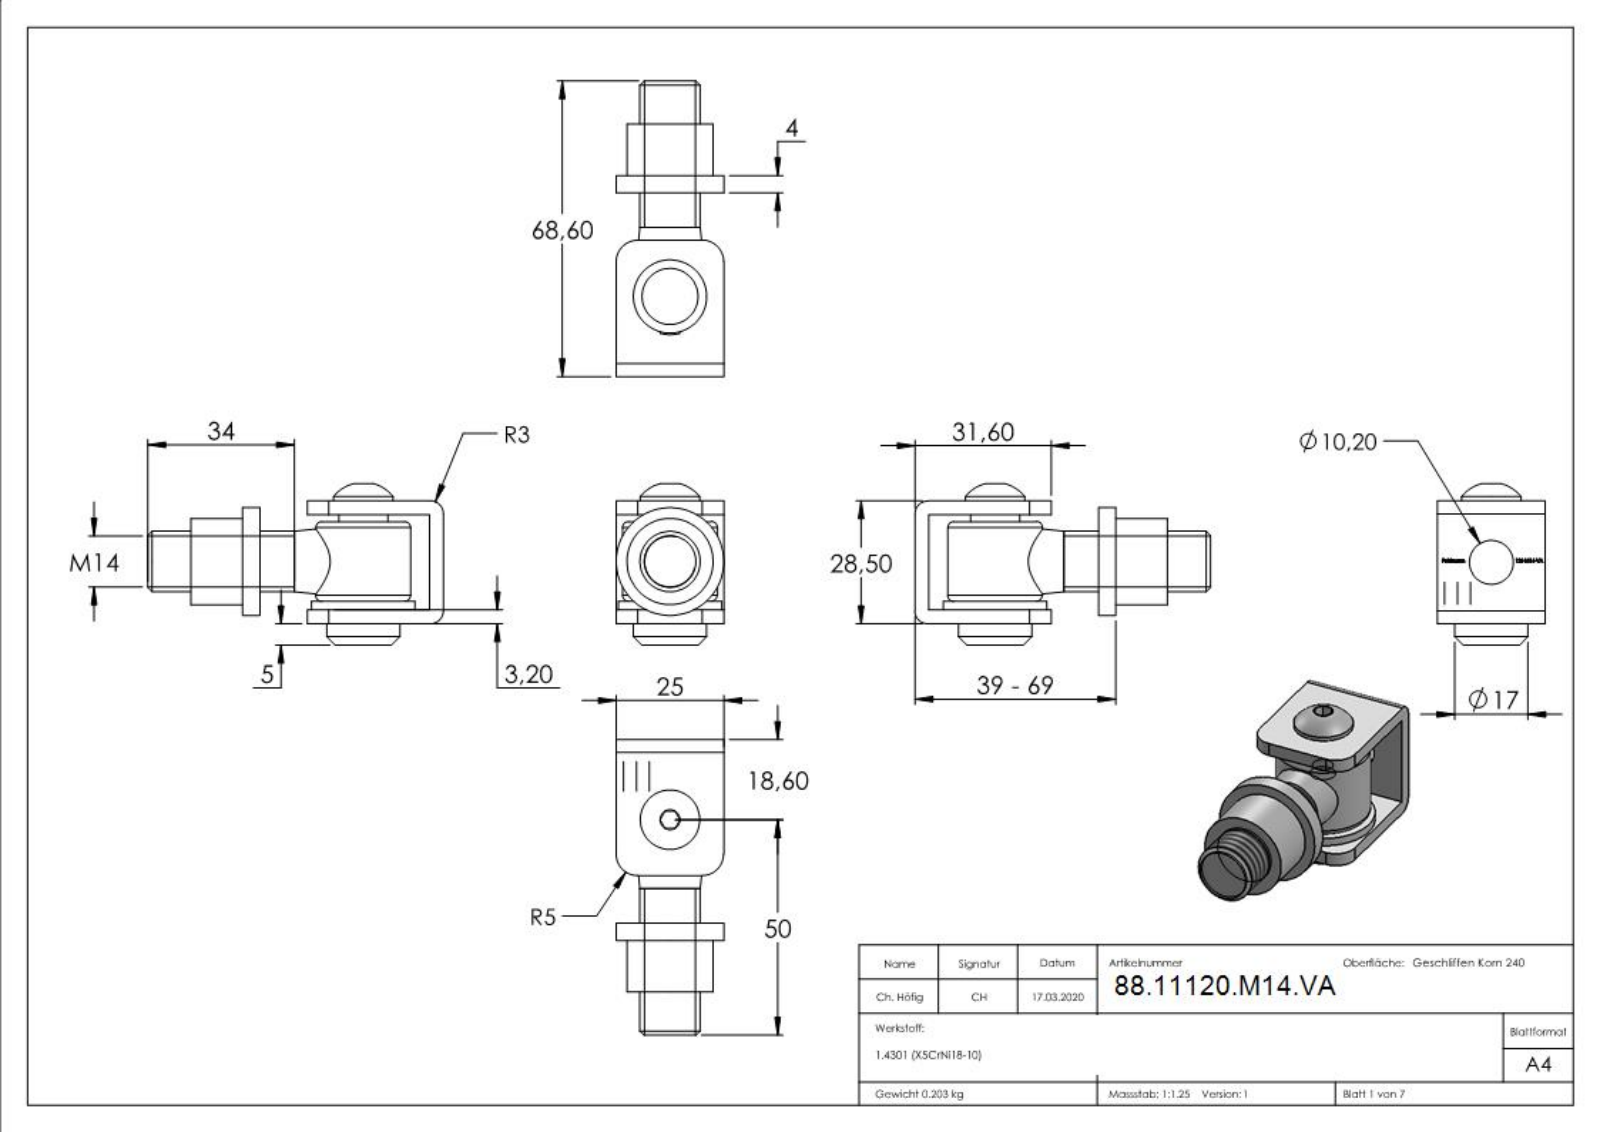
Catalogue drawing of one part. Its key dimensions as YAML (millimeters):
part_name: "120-M14-VA Teil5_120-M14-VA Teil5; 120-M14-VA Teil5; 120-M14-VA Teil1_120-M14-VA Teil1; 120-M14-VA Teil1 (+8 more)"
step_written_by: "SolidWorks 2015 (CONFIG_CONTROL_DESIGN)"
units: millimeters
bodies: {solids: 6, faces: 286, planar: 183, cylindrical: 24, other: 79}
overall_size: [68.6, 37.5, 25]
volume: 25665
surface_area: 14442
round_holes:
  - {diameter: 5, count: 1}
  - {diameter: 6.8, count: 1}
  - {diameter: 10.2, count: 1}
  - {diameter: 11.6, count: 1}
  - {diameter: 11.8, count: 1}
  - {diameter: 12, count: 1}
  - {diameter: 13, count: 1}
round_bosses_or_shafts:
  - {diameter: 25, count: 1}
  - {diameter: 24, count: 1}
  - {diameter: 22, count: 1}
  - {diameter: 20, count: 1}
  - {diameter: 17, count: 1}
  - {diameter: 14, count: 1}
  - {diameter: 13.8, count: 1}
  - {diameter: 11.4, count: 1}
partial_cylinders:
  - {radius: 3, count: 2}
  - {radius: 5, count: 2}
  - {radius: 8.9, count: 1}
face_to_face_distances: [3.2, 25.3, 28.5, 22.1, 5.2, 2, 20.1, 23.3, 42.6, 39.4]
